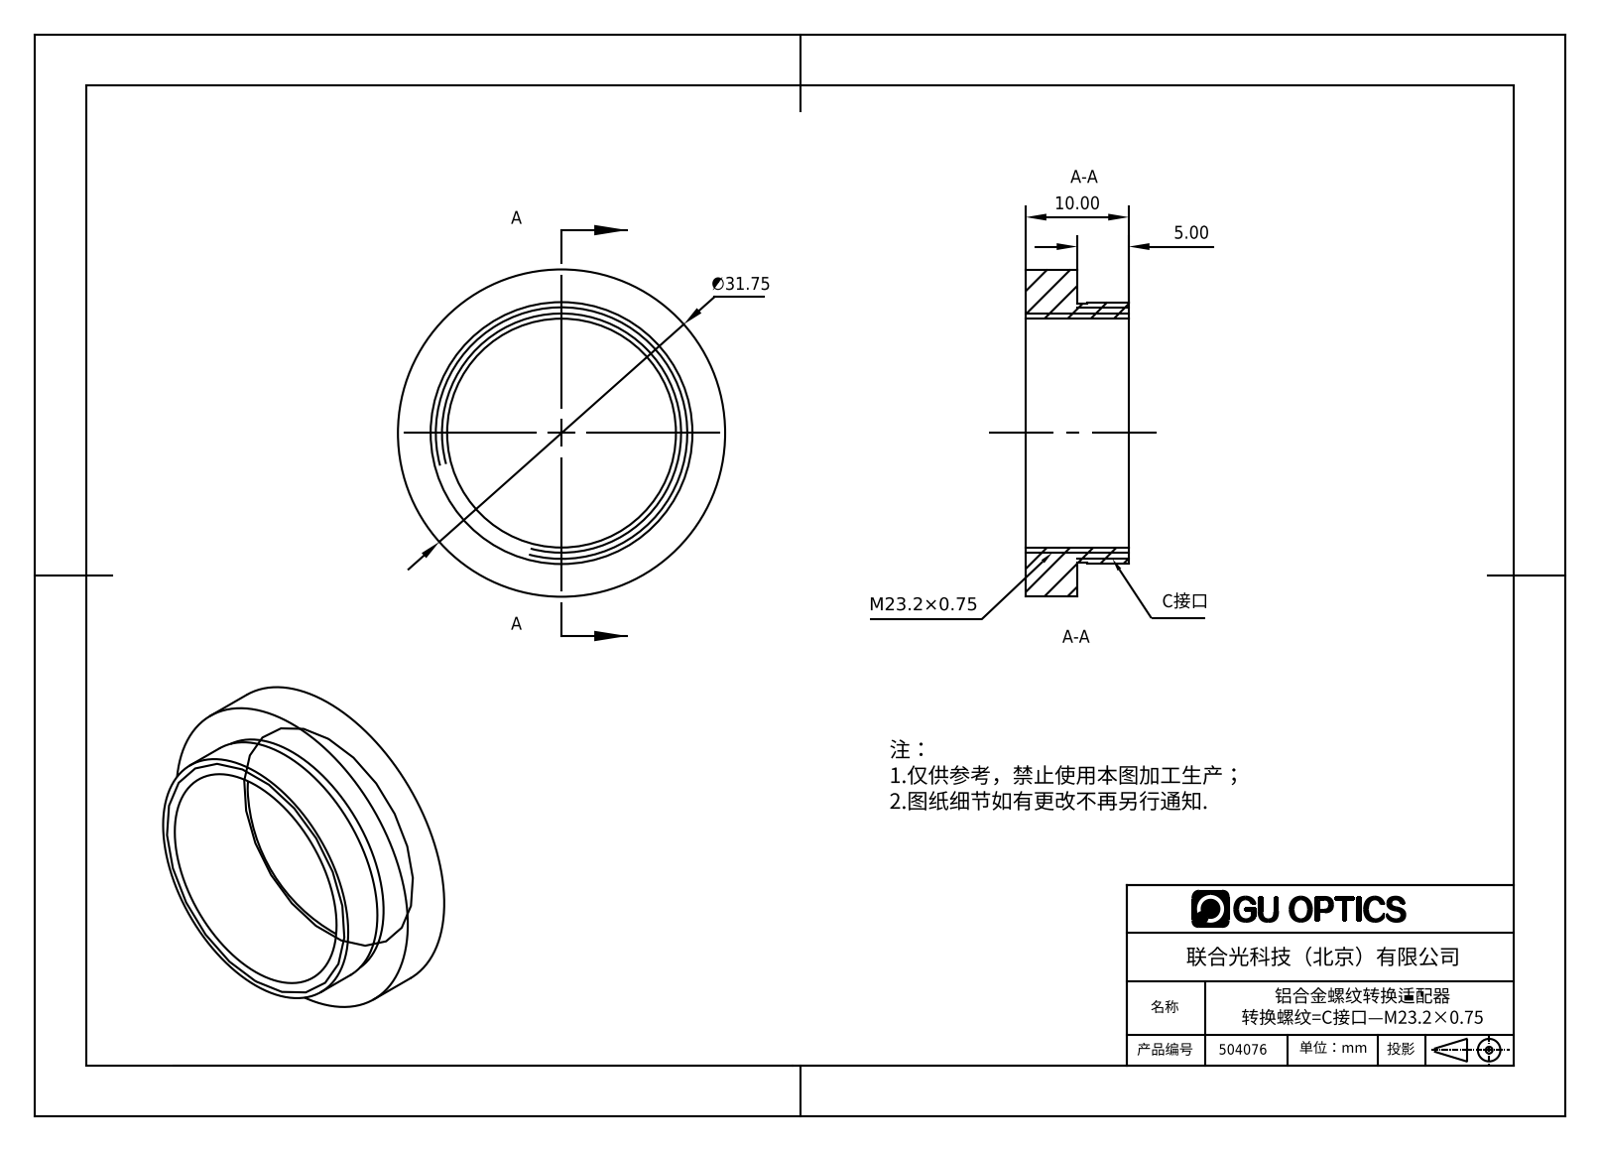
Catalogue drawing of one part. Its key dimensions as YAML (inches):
part_name: "504086"
step_written_by: "SolidWorks 2016 (AUTOMOTIVE_DESIGN)"
units: inches
bodies: {solids: 1, faces: 9, planar: 3, cylindrical: 6, other: 0}
overall_size: [1, 1, 0.394]
volume: 0.19
surface_area: 2.959
round_holes:
  - {diameter: 0.551, count: 1}
round_bosses_or_shafts:
  - {diameter: 1, count: 1}
  - {diameter: 0.913, count: 1}
face_to_face_distances: [0.394, 0.197]
